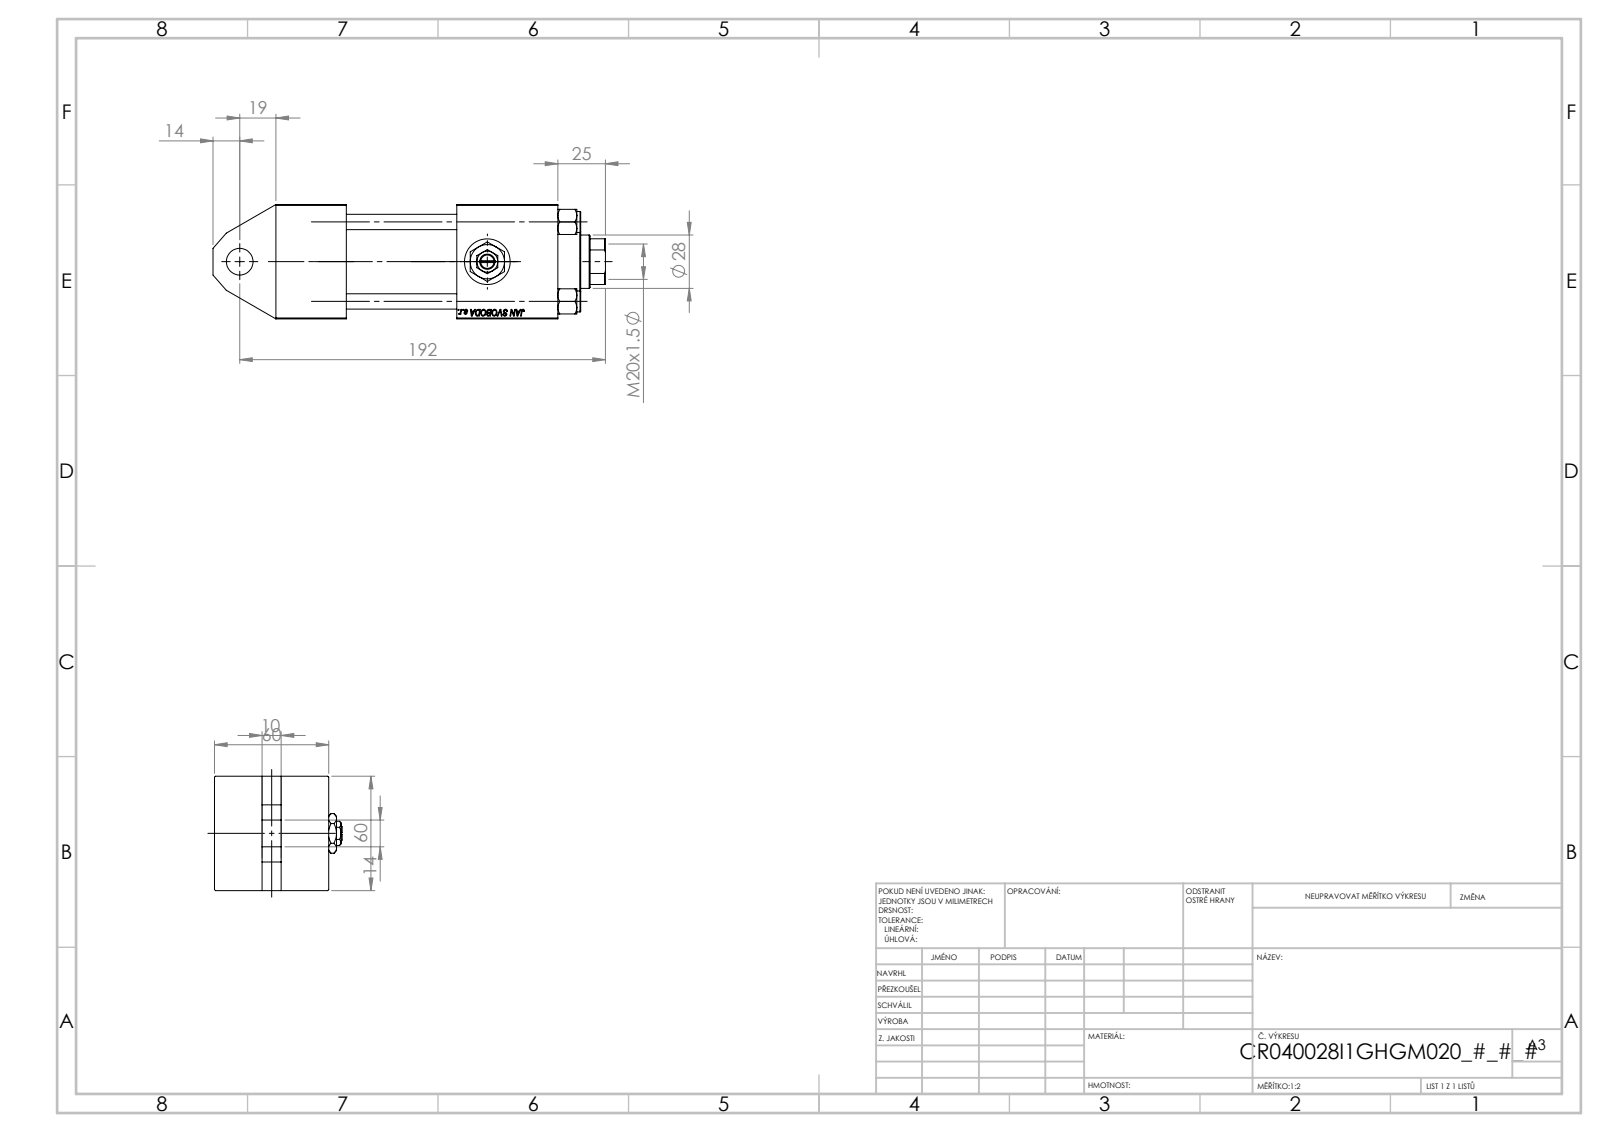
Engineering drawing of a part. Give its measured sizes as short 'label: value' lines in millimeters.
name: V215CR_I_Body; V215_VC_A; V215CR_VCP_I; V215CR_TYCINKA_I (+2 more)
written by: SolidWorks 2019 (CONFIG_CONTROL_DESIGN)
unit: mm
bodies: 12 solids, 1133 faces (525 planar, 88 cylindrical, 520 other)
size: 206 × 67 × 60
volume: 436 411 mm³; area: 116 665 mm²
holes: 4× ⌀8, 2× ⌀7, 2× ⌀16.66, 2× ⌀24, 1× ⌀14, 1× ⌀18.5, 1× ⌀28, 1× ⌀31, 1× ⌀40, 1× ⌀45
bosses: 4× ⌀11, 1× ⌀46, 1× ⌀42
rounds: 2× R1.25, 1× R13.5
face distances: 60, 37, 53, 58, 25, 95, 35, 148, 111, 119.3
hole spacings: 29.49, 41.7, 58.97, 37.5, 92.5, 130
